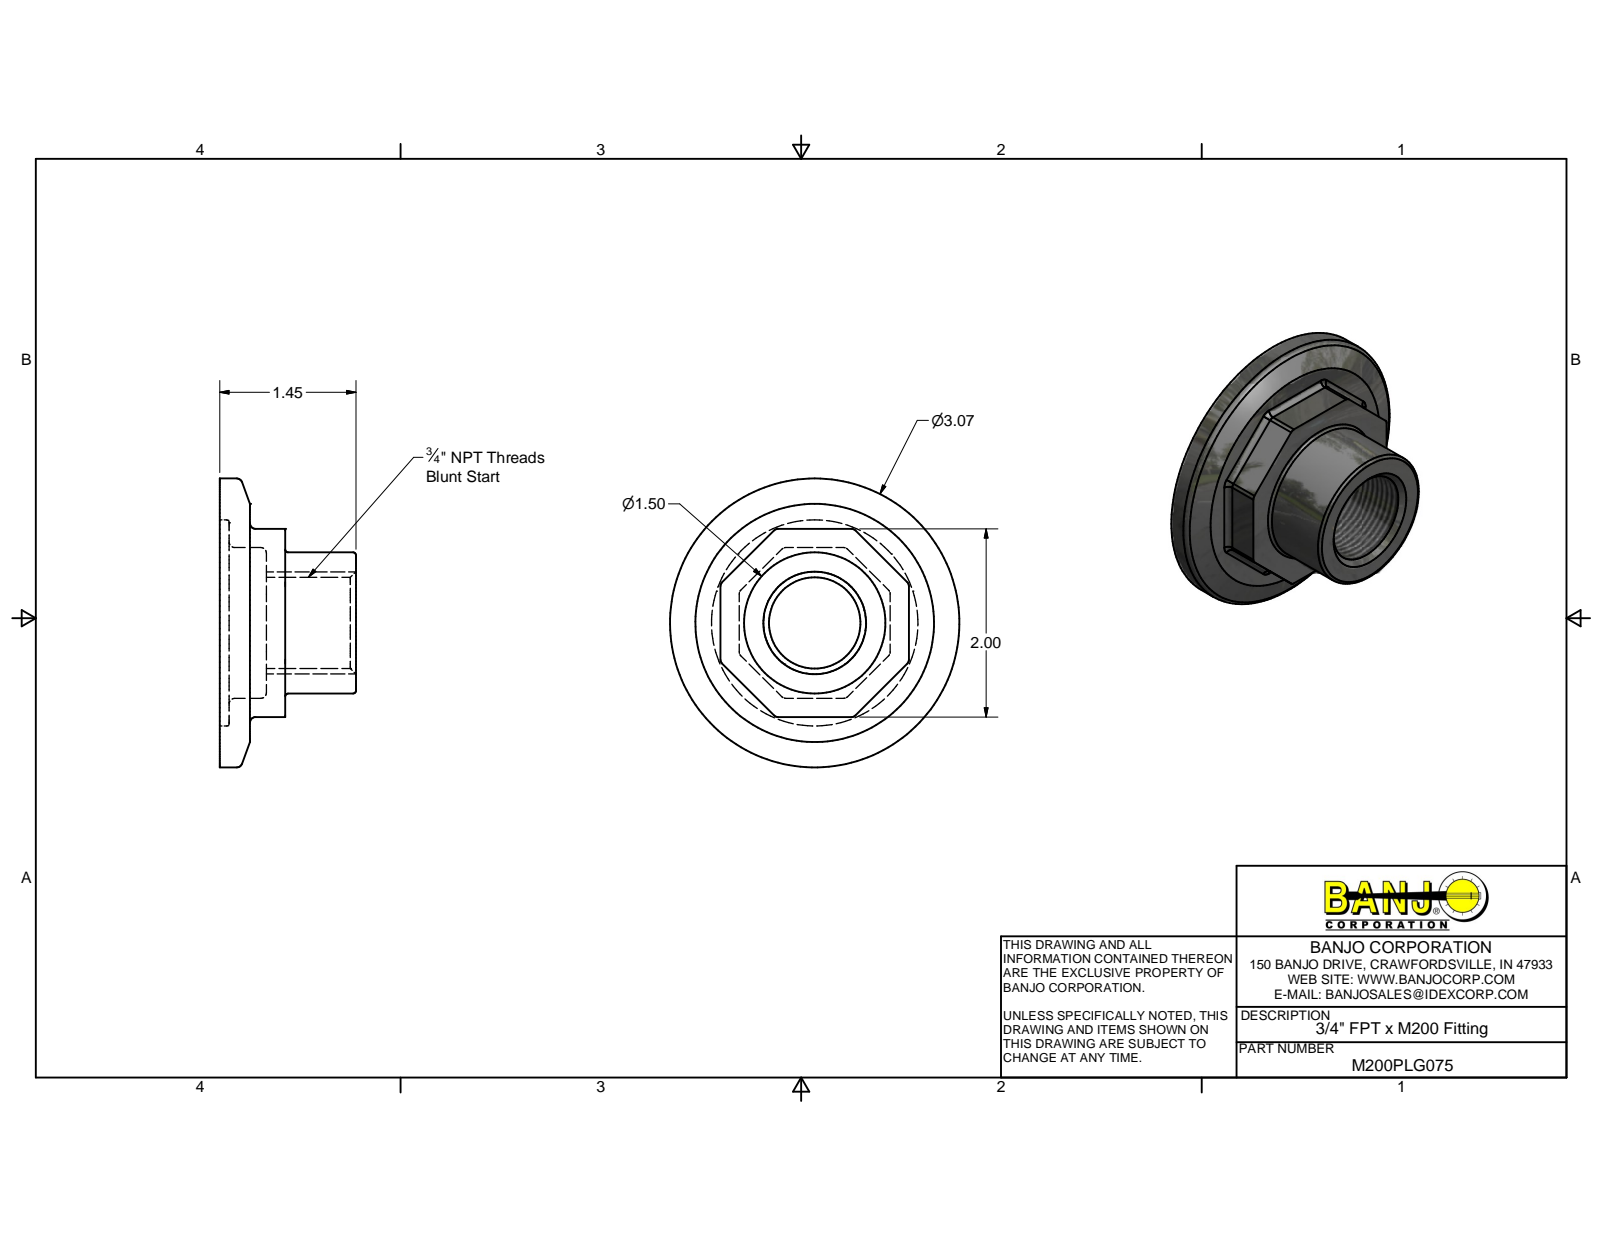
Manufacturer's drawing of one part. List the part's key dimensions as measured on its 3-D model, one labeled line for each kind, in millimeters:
Part name (STEP PRODUCT): DRAWING3
STEP written by: Mechanical Desktop 2009 (CONFIG_CONTROL_DESIGN)
Units: millimetres
Bodies: 1 solid, 88 faces (18 planar, 36 cylindrical, 34 other)
Overall size (bounding box): 3.07 × 3.07 × 1.45
Volume: 3 mm³ · Surface area: 27 mm²
Round holes (diameter × count): ⌀2.19 ×1
Round bosses / shafts (diameter × count): ⌀3.07 ×1, ⌀1.5 ×1
Main face-to-face distances: 0.69, 1.8, 0.49, 0.32, 0.37, 2, 0.39, 0.59, 1.6, 1.45
